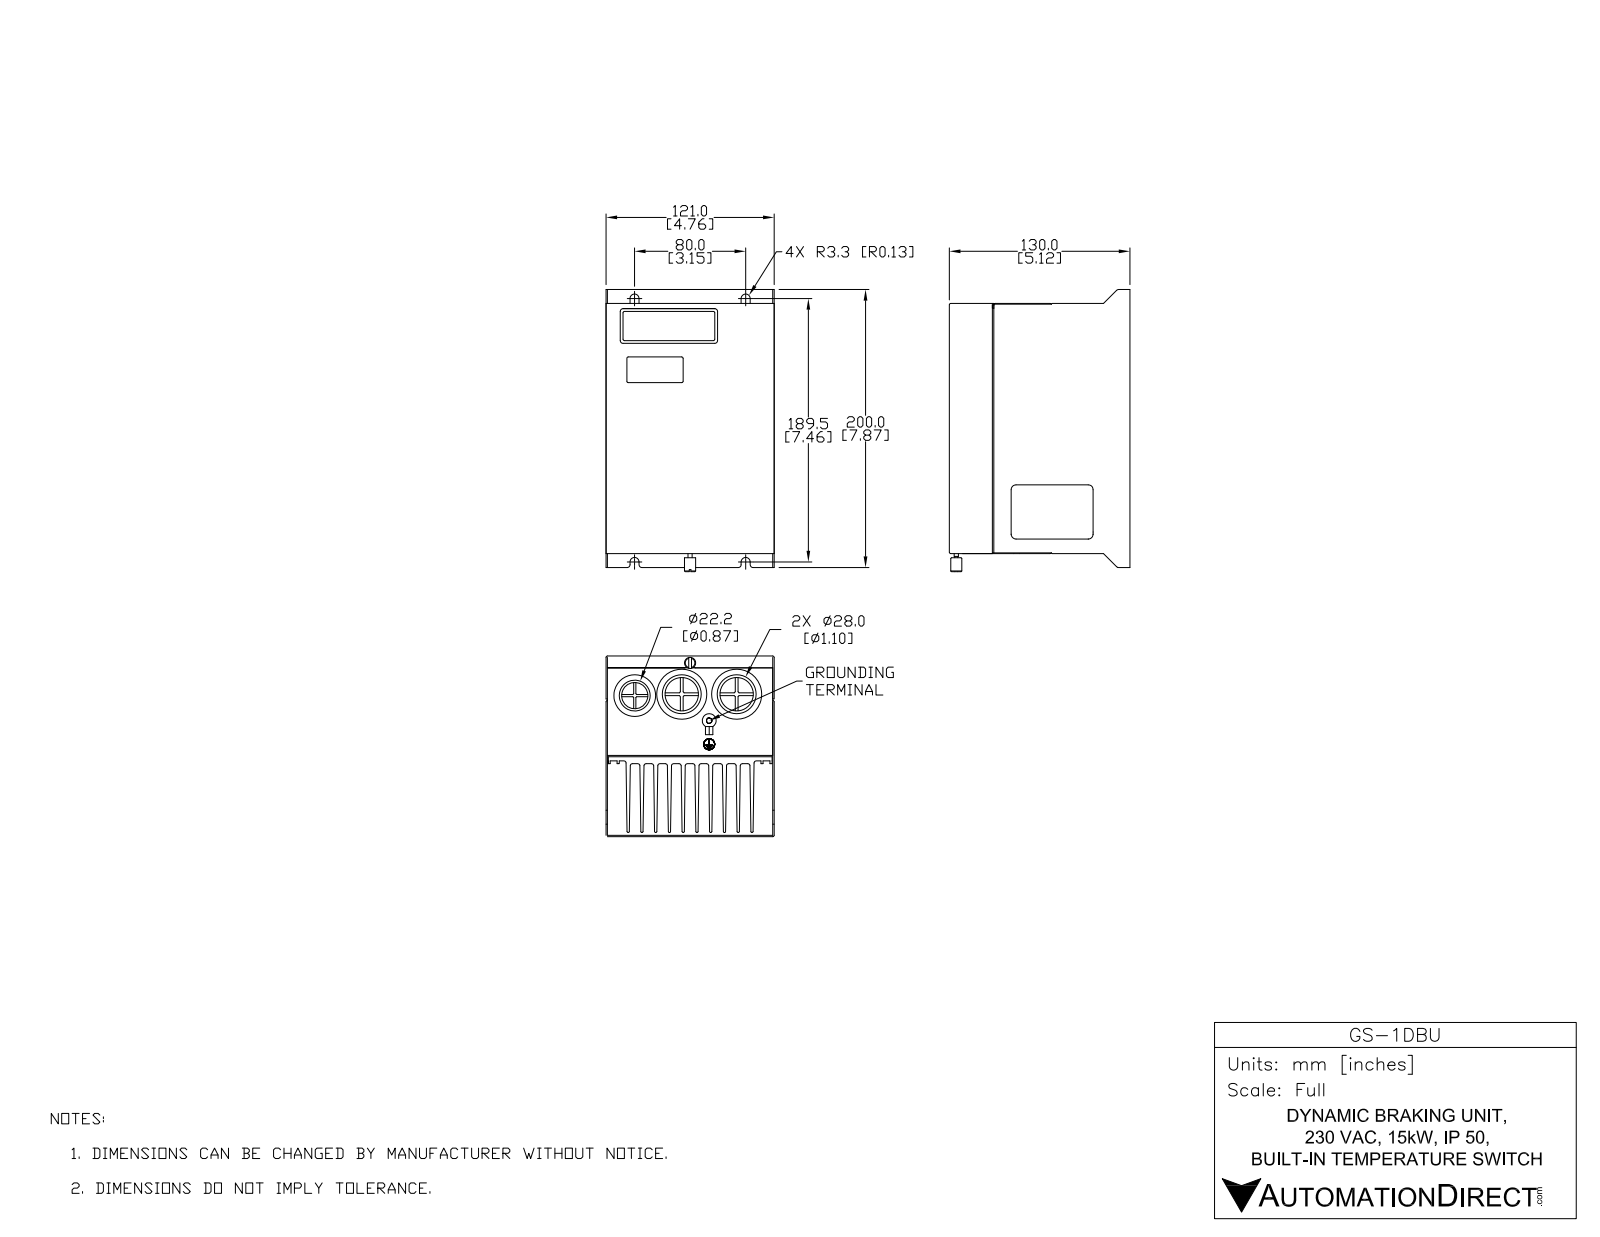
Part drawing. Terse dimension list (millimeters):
name: GS-1DBU
written by: SolidWorks 2015 (AUTOMOTIVE_DESIGN)
unit: mm
bodies: 26 solids, 1178 faces (782 planar, 293 cylindrical, 103 other)
size: 203.2 × 129.5 × 121
volume: 414 100 mm³; area: 505 000 mm²
holes: 2× ⌀27.5, 1× ⌀3, 1× ⌀3.7, 1× ⌀10, 1× ⌀21.5
bosses: 5× ⌀10, 4× ⌀7, 4× ⌀2.4, 3× ⌀7.6, 3× ⌀1, 2× ⌀37, 2× ⌀29.5, 2× ⌀25
rounds: 45× R2, 16× R0.8, 16× R1, 14× R0.7, 11× R0.5, 7× R1.5, 4× R0.5, 4× R3.3
face distances: 1, 9.1, 120, 56.5, 1.5, 18.2, 7.6, 10.6, 47.5, 38.4
hole spacings: 4, 24.1, 27.4, 27.4, 33.8, 35.7, 37.7, 39.5
